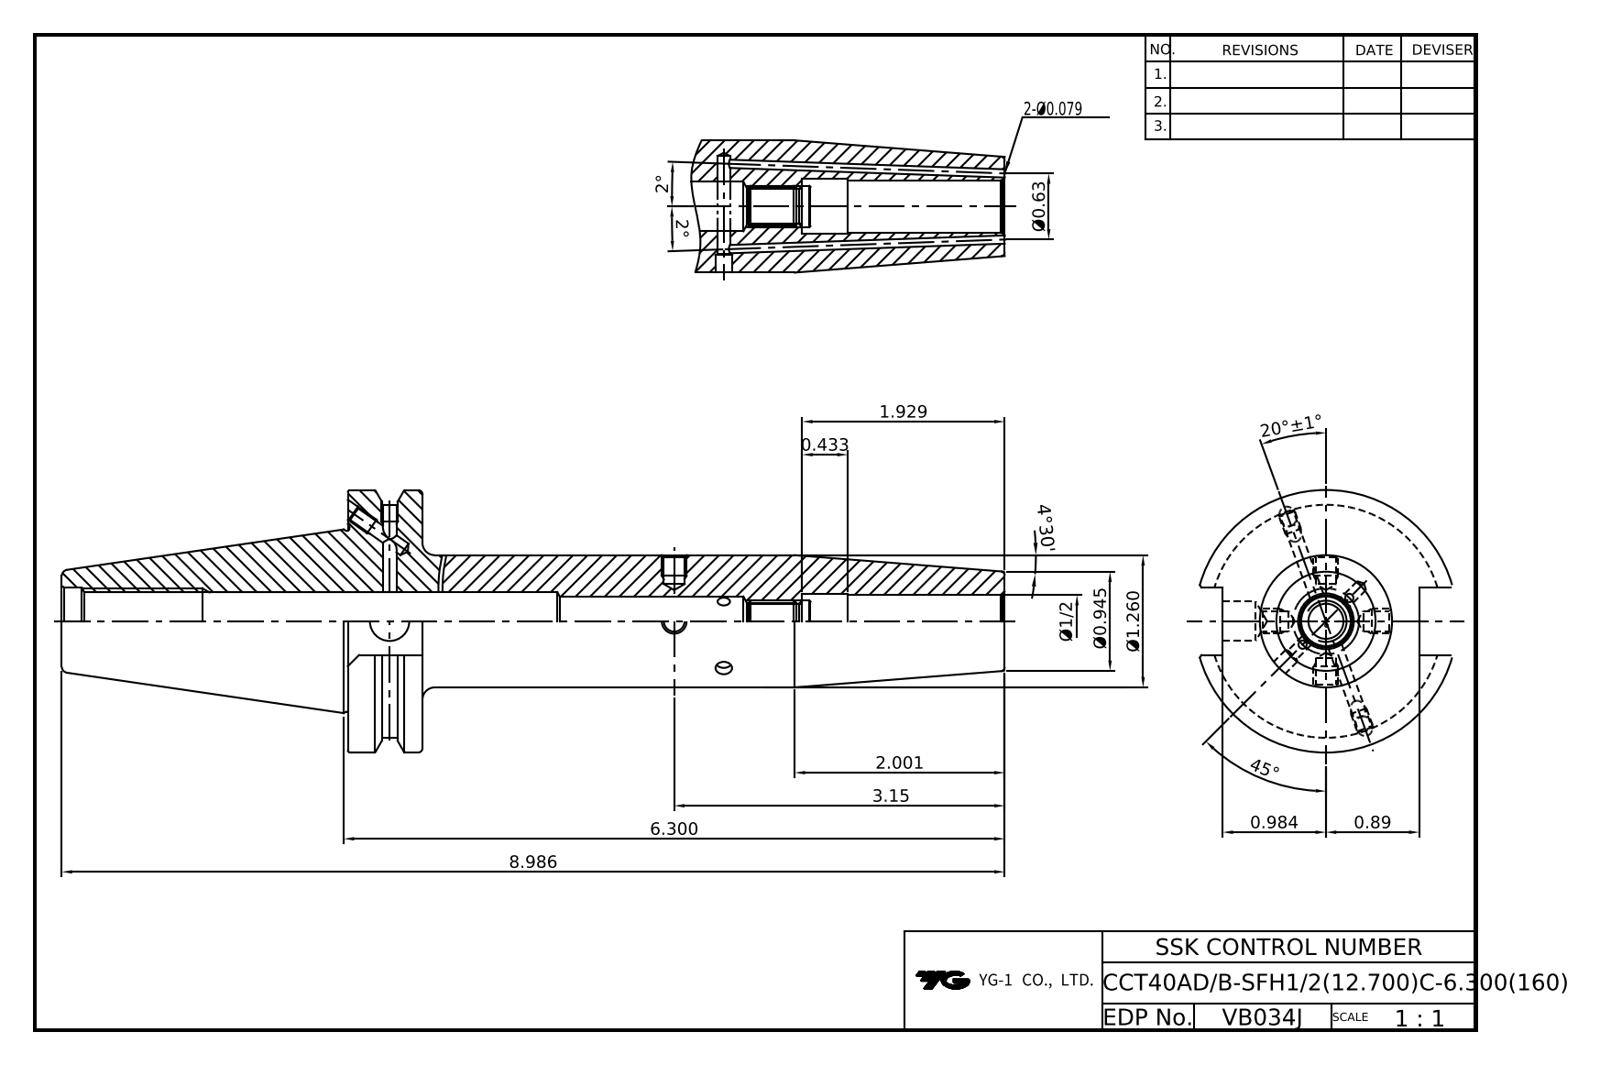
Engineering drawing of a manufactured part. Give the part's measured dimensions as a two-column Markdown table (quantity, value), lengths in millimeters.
| quantity | value |
| --- | --- |
| part name | LO CCT40ADB-SFH12.7C-6.30 |
| STEP written by | Autodesk Inventor 2022 (AUTOMOTIVE_DESIGN) |
| units | millimeters |
| bodies | 1 solid, 110 faces (38 planar, 38 cylindrical, 34 other) |
| overall size | 228.25 × 63.5 × 61.09 |
| volume | 189 824 mm³ |
| surface area | 40 964 mm² |
| round holes (diameter × count) | 3.24 × 4, 4 × 3, 2.5 × 2, 4.2 × 2, 4.92 × 2, 3 × 1, 8.92 × 1, 9.53 × 1, 12.7 × 1, 13 × 1, 13.39 × 1, 13.9 × 1 |
| round bosses / shafts (diameter × count) | 63.5 × 1, 43.8 × 1, 32 × 1 |
| partial cylindrical surfaces (radius × count) | 28.15 × 1 |
| main face-to-face distances | 18.05, 47.6, 159, 140.95, 16.38, 69.25, 87.3, 228.25, 81.34, 12.09 |
| hole center spacings | 93.82 |
